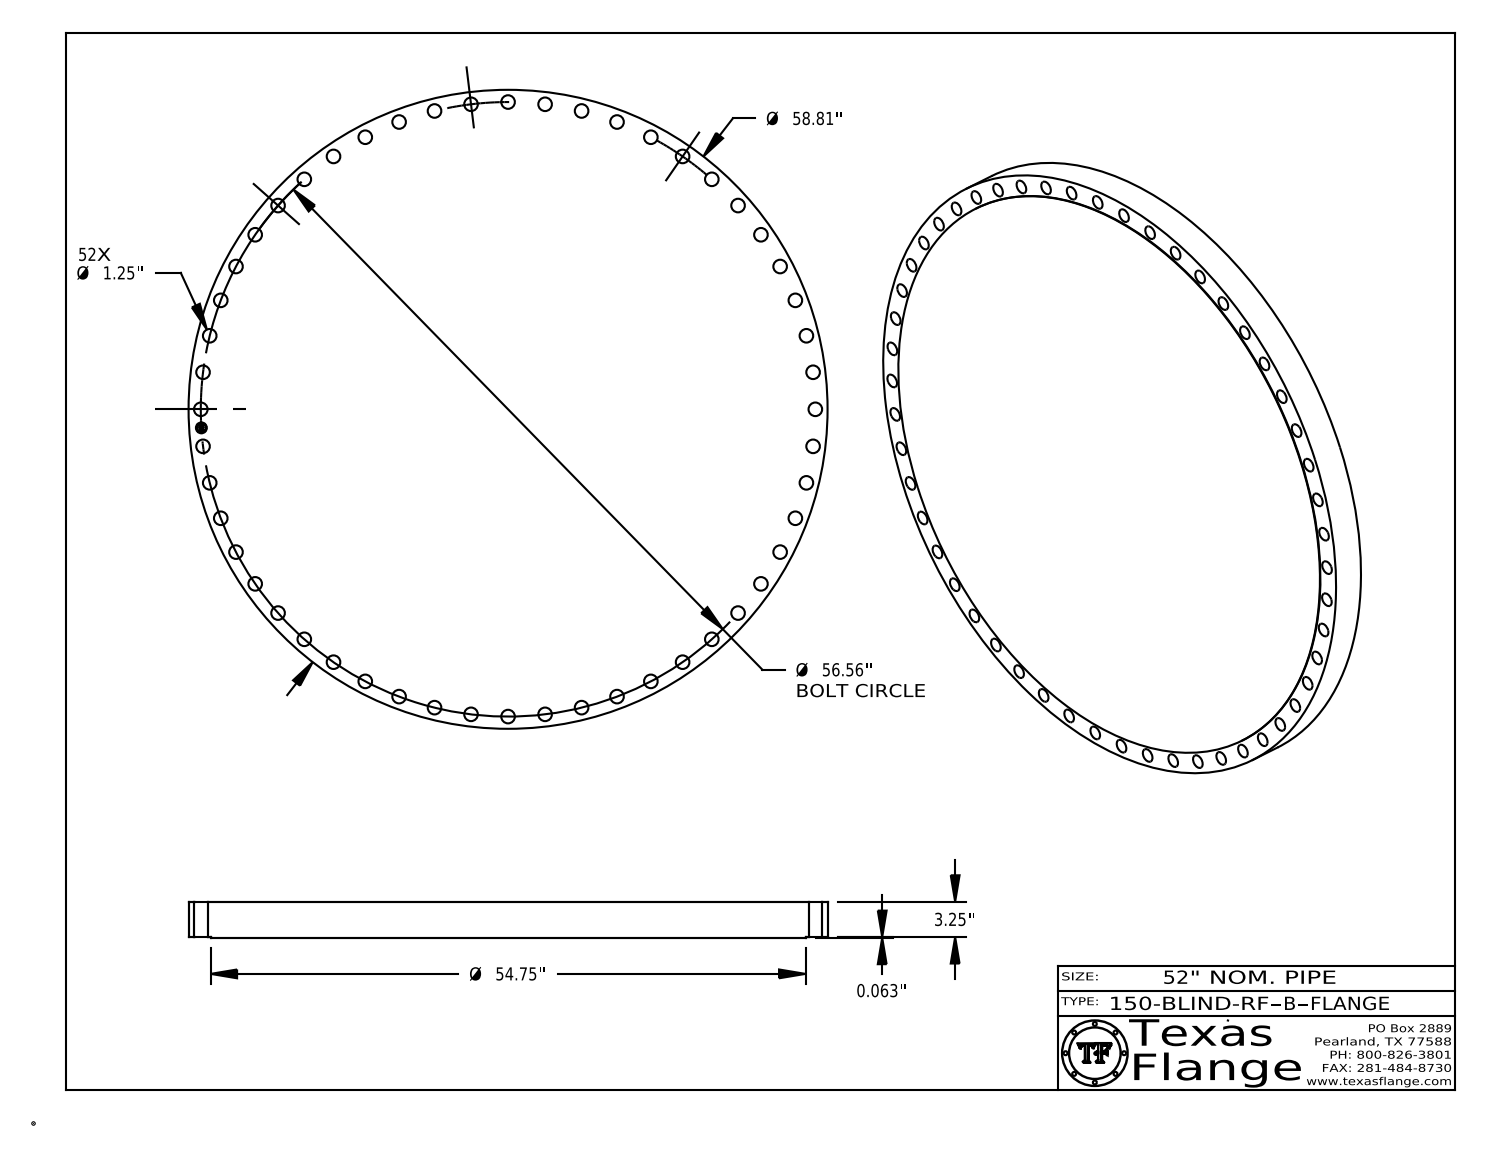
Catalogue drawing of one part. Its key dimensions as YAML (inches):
part_name: "150-BLIND-RF, Series B"
step_written_by: "CATIA V5 STEP AP214 (AUTOMOTIVE_DESIGN)"
units: inches
bodies: {solids: 1, faces: 496, planar: 368, cylindrical: 128, other: 0}
overall_size: [58.81, 58.81, 3.313]
volume: 8769
surface_area: 6580
round_holes:
  - {diameter: 1.25, count: 52}
  - {diameter: 1, count: 1}
round_bosses_or_shafts:
  - {diameter: 0.061, count: 8}
  - {diameter: 58.81, count: 1}
  - {diameter: 54.75, count: 1}
  - {diameter: 0.788, count: 1}
face_to_face_distances: [3.313, 0.063, 3.25, 3.298, 3.235, 0.015, 0.298, 0.293, 0.019, 0.054]
hole_center_spacings: [56.457, 3.415, 56.148, 6.817, 55.633, 10.195, 16.827, 53.999]
